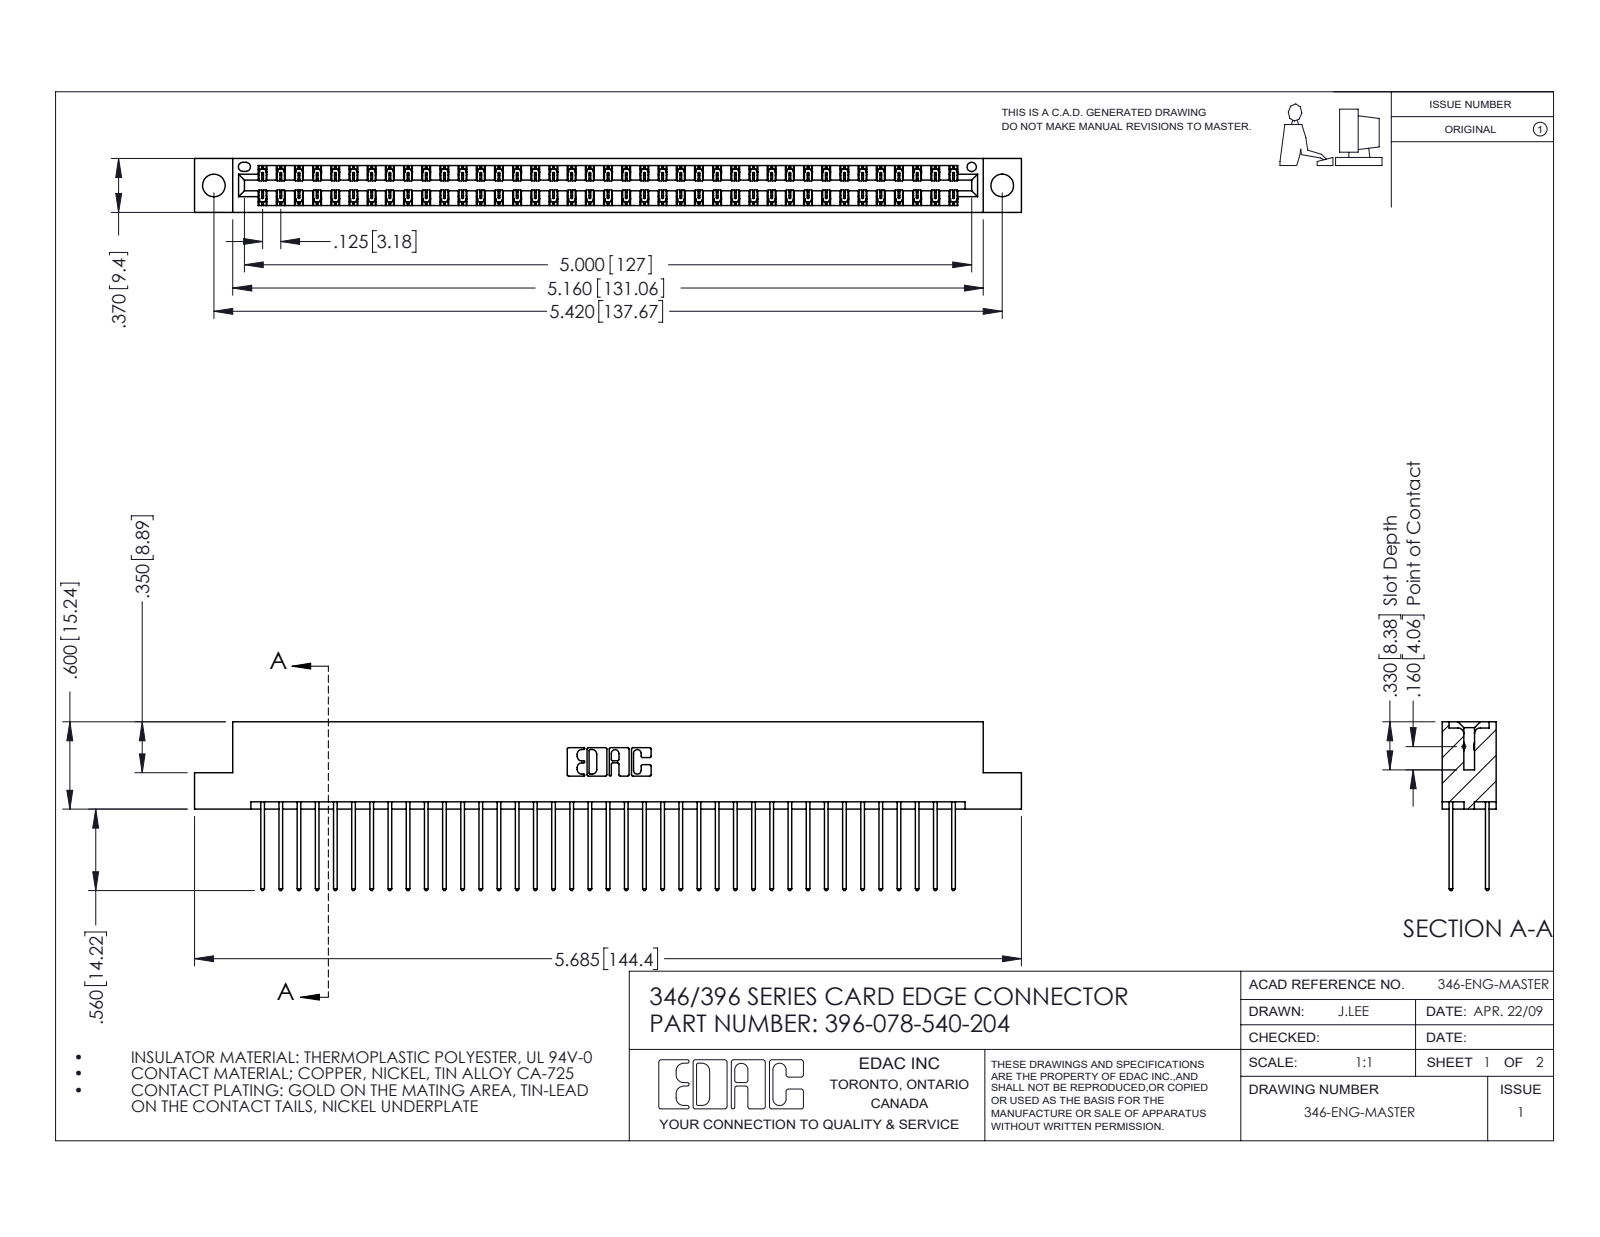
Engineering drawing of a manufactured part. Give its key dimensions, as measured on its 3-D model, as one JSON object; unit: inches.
{"part_name": "345-292-001_345-293-140; 346 Part_Flush Mounting Lugs - 0.156 Dia-TH; 396-078-540-204", "step_written_by": "SolidWorks 2016 (CONFIG_CONTROL_DESIGN)", "units": "inches", "bodies": {"solids": 79, "faces": 4178, "planar": 2806, "cylindrical": 1372, "other": 0}, "overall_size": [5.685, 1.16, 0.37], "volume_in3": 0.871, "surface_area_in2": 32.2, "round_holes": [[0.156, 2], [0.064, 1]], "partial_cylinders_radius": [[0.006, 117], [0.01, 78], [0.01, 22], [0.007, 6], [0.031, 6], [0.026, 3], [0.014, 2], [0.022, 2]], "face_to_face_distances": [0.048, 0.322, 0.25, 0.072, 0.298, 0.025, 0.37, 0.275, 0.148, 0.222], "hole_center_spacings": [0.246, 5.211, 5.42]}
